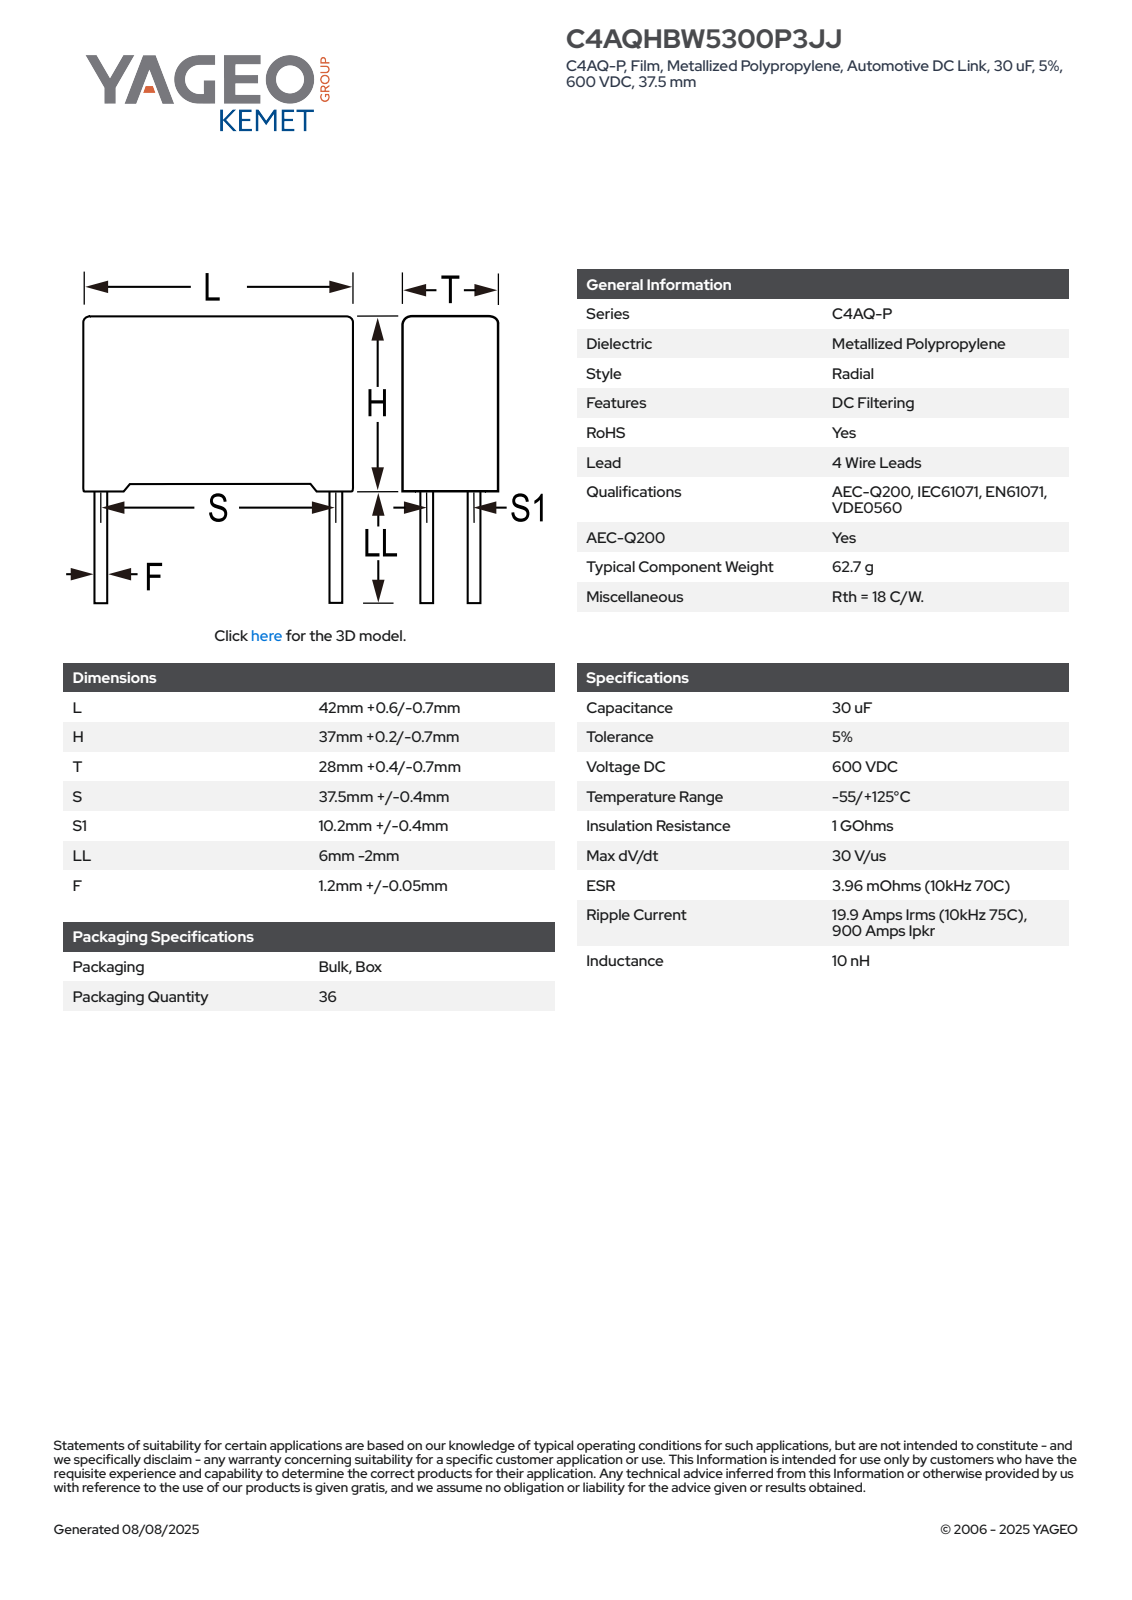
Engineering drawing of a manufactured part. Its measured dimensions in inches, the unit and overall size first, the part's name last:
Units: inches
Overall size (bounding box): 1.677 × 1.622 × 1.119
Round bosses / shafts (diameter × count): ⌀0.049 ×4
Main face-to-face distances: 1.118, 1.422, 1.677, 0.043, 1.465, 0.069, 1.119, 1.608, 1.539, 1.049
Volume: 2.677 in³ · Surface area: 12.28 in²
Bodies: 4 solids, 87 faces (79 planar, 8 cylindrical, 0 other)
Part name (STEP PRODUCT): CFP_RB4_42X37X28_L42.6H37.2T28.4S37.5S110.2LL4F1.25
STEP written by: SolidWorks 2014 (AUTOMOTIVE_DESIGN)
